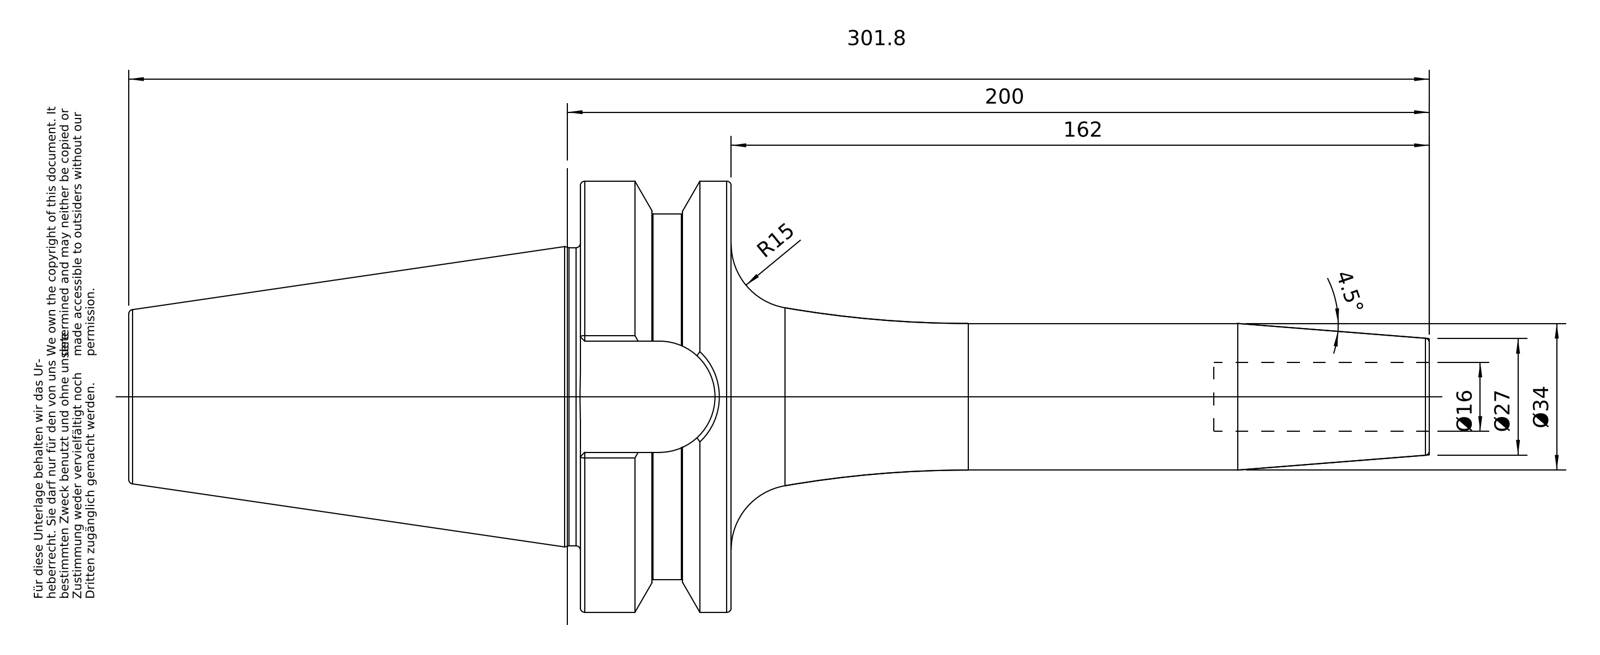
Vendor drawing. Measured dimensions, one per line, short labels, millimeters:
name: 50-646-16
written by: PRO/ENGINEER BY PARAMETRIC TECHNOLOGY CORPORATION, 2010430 (CONFIG_CONTROL_DESIGN)
unit: mm
bodies: 1 solid, 98 faces (26 planar, 22 cylindrical, 50 other)
size: 301.8 × 99.97 × 99.97
volume: 615 394 mm³; area: 70 308 mm²
holes: 1× ⌀16, 1× ⌀20.75, 1× ⌀25.02, 1× ⌀25.7
bosses: 1× ⌀99.97, 1× ⌀84.75, 1× ⌀69.15, 1× ⌀34, 1× ⌀24.01
rounds: 1× R12.9
face distances: 35, 70.4, 104.8, 139.8, 25.8, 301.8, 197, 162, 251.8, 147
